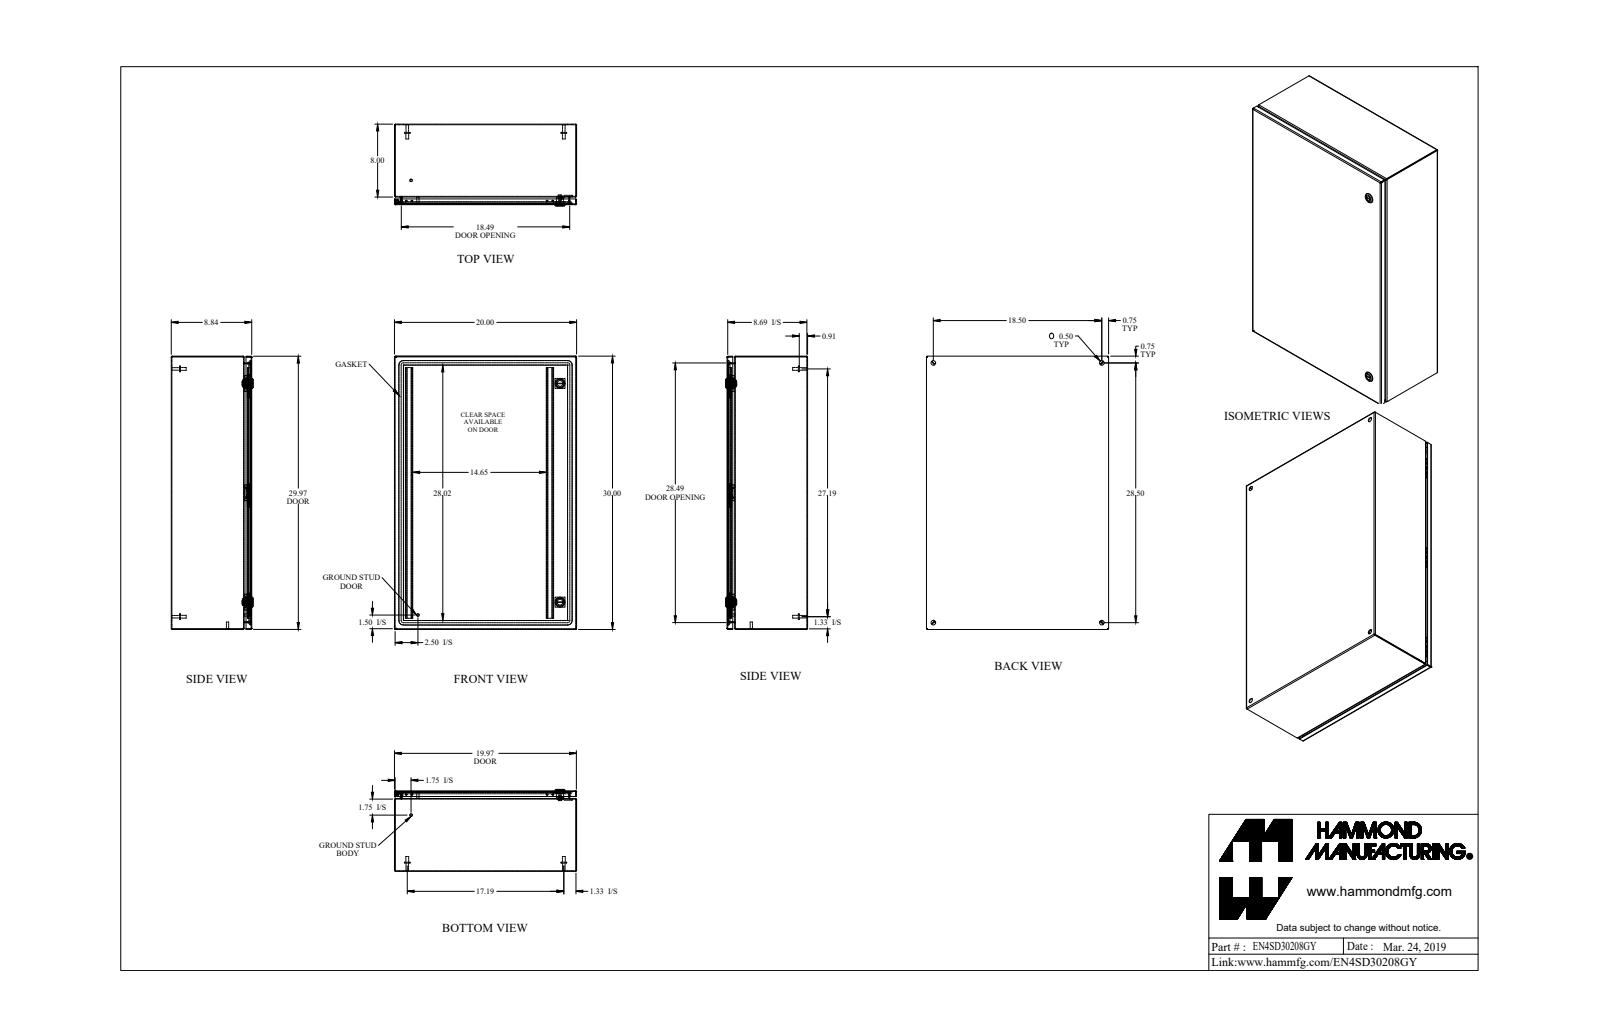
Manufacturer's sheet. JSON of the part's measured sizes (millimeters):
{"part_name": "EN4SD30208GY_Default", "step_written_by": "SolidWorks 2019 (CONFIG_CONTROL_DESIGN)", "units": "millimeters", "bodies": {"solids": 31, "faces": 885, "planar": 422, "cylindrical": 295, "other": 168}, "overall_size": [762, 508, 228.5], "volume_mm3": 2815000, "surface_area_mm2": 3115000, "round_holes": [[12.7, 4], [5.9, 2], [15.9, 2], [19.9, 2], [4.4, 1], [6.1, 1], [6.1, 1]], "round_bosses_or_shafts": [[15.9, 4], [8, 4], [6.9, 4], [27.9, 2], [13.3, 2], [7.1, 2], [6.4, 2], [11.6, 1]], "partial_cylinders_radius": [[0.9, 20], [2.7, 20], [1.1, 12], [2.1, 12], [9.7, 12], [482.7, 8], [0.2, 6], [1.6, 6]], "face_to_face_distances": [1.8, 222.6, 220.8, 224.5, 506.2, 760.2, 504.3, 508, 758.3, 762], "hole_center_spacings": [469.9, 723.9, 863, 63.3, 63.3, 446.3, 446.3, 609.6]}
